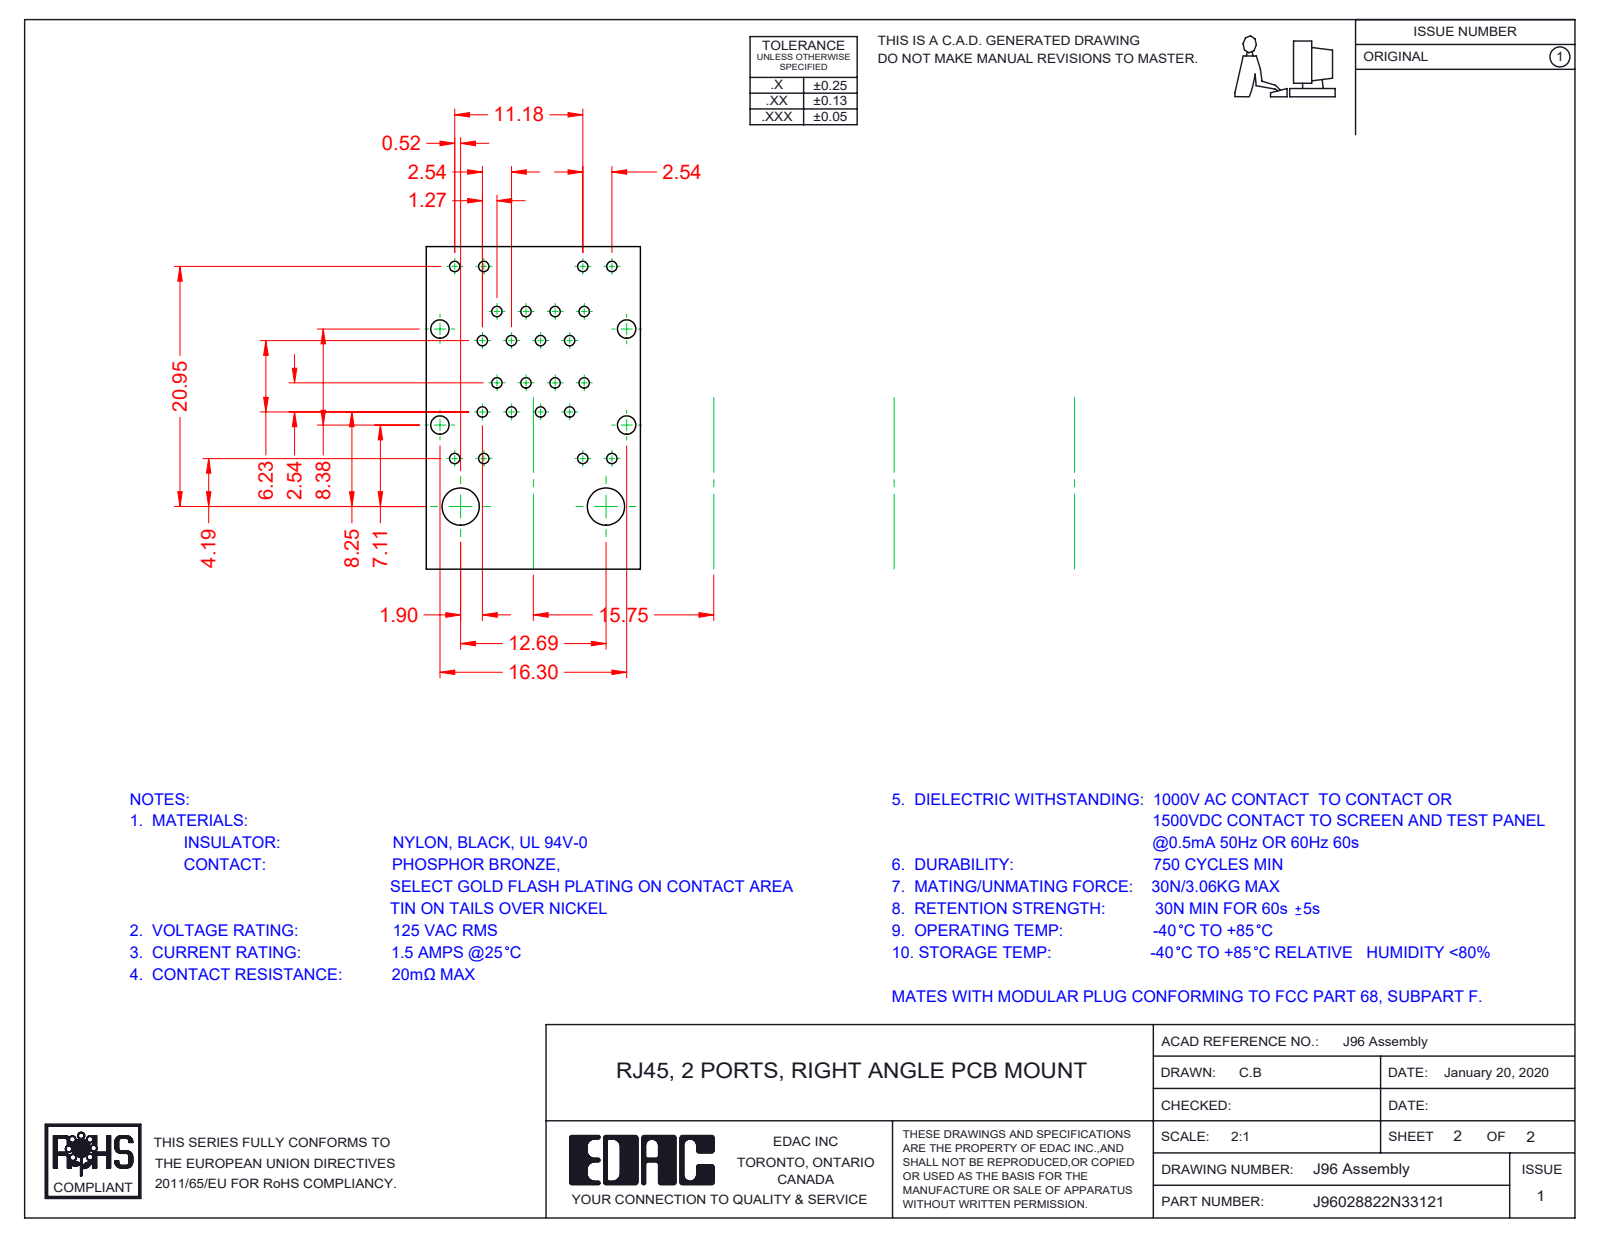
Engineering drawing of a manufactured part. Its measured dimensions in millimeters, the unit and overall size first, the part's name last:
Units: millimetres
Overall size (bounding box): 29.58 × 28.68 × 16.8
Partial cylindrical surfaces — rounded edges, fillets, slot ends (radius × count): R0.25 ×48, R0.15 ×32, R0.35 ×24, R0.5 ×16, R1 ×16, R0.2 ×13, R0.7 ×9, R2 ×5
Main face-to-face distances: 16.3, 16.1, 1.75, 16.5, 14.75, 1.55, 14.55, 0.53, 1.48, 11.2
Volume: 6 852 mm³ · Surface area: 19 109 mm²
Bodies: 27 solids, 2382 faces (1849 planar, 427 cylindrical, 106 other)
Part name (STEP PRODUCT): 96 Shield_2 Ports LED - No EMI; 96 Insulator_2 Ports; 96 Contact Lock Upper; 96 Back Plate_2 Ports (+8 more)
STEP written by: SolidWorks 2016 (CONFIG_CONTROL_DESIGN)
